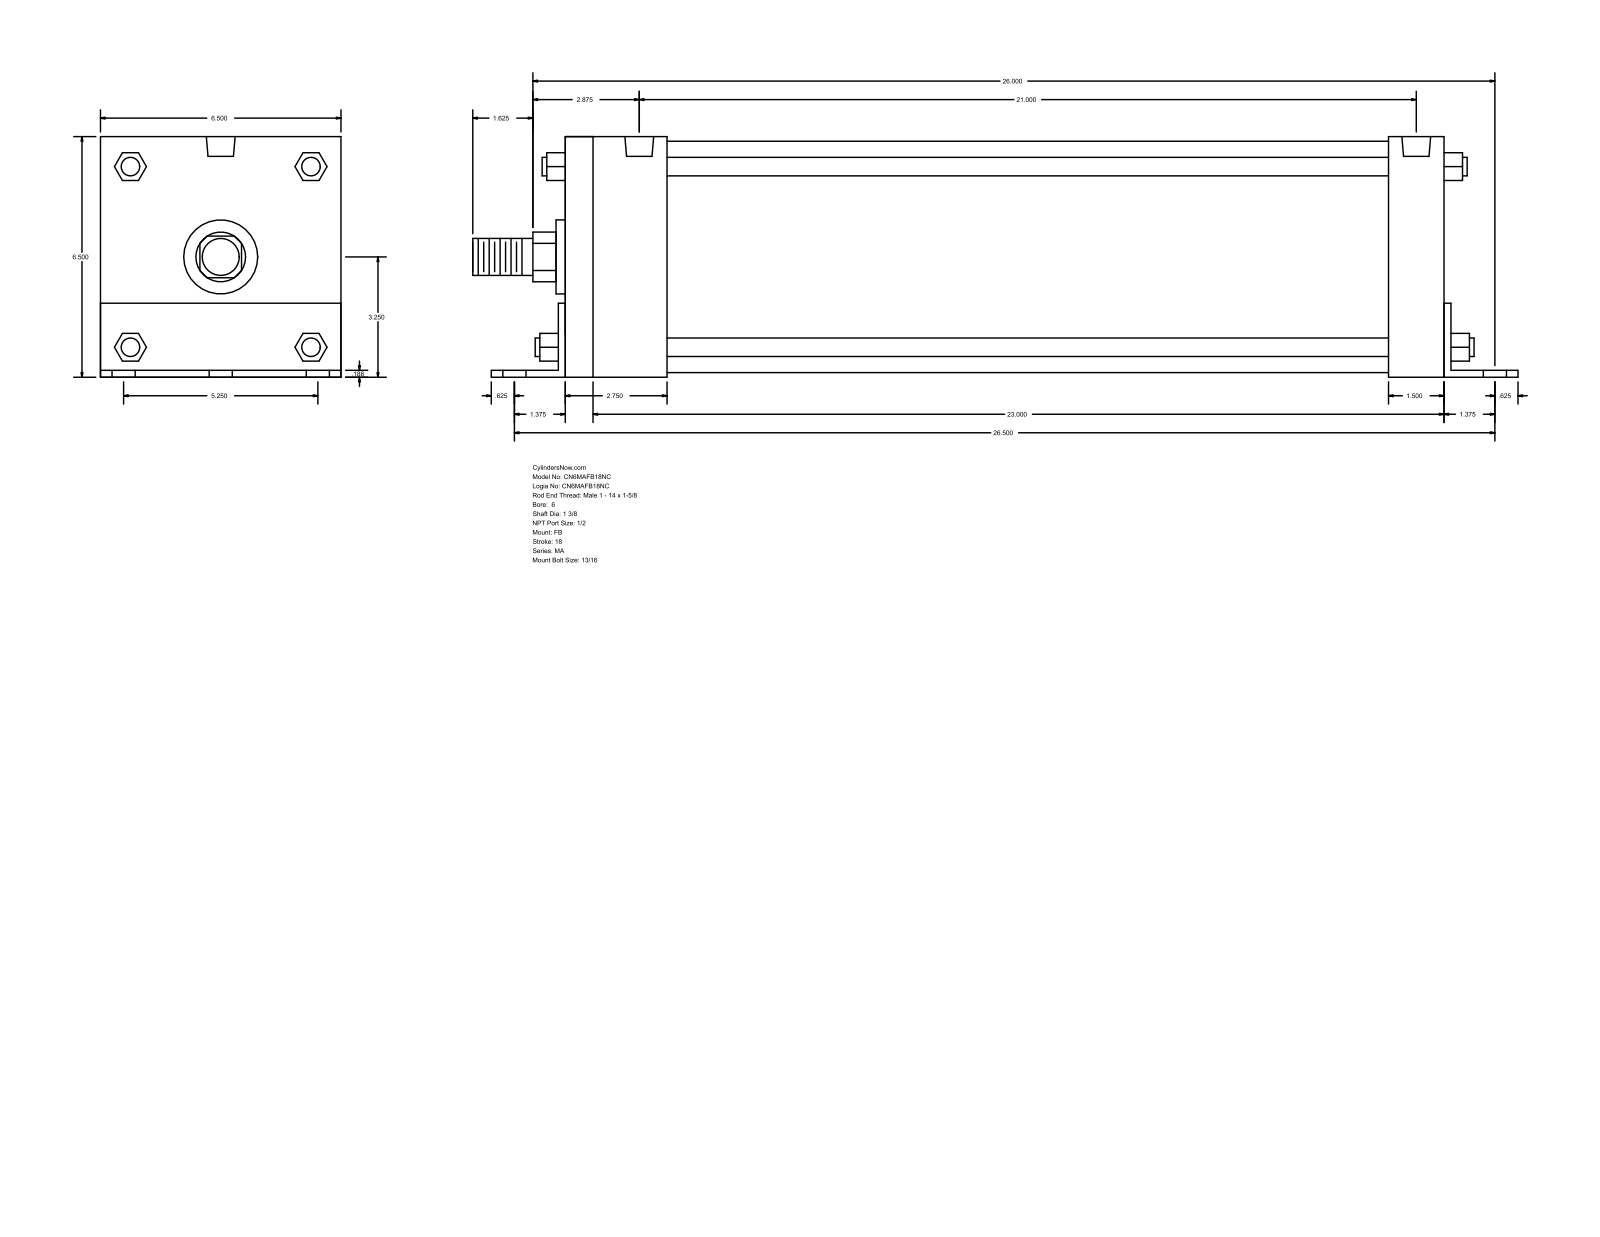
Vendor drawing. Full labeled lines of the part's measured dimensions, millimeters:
Part name (STEP PRODUCT): MA_FB__0600_1.375
STEP written by: GSSL Pune (CONFIG_CONTROL_DESIGN)
Units: millimetres
Bodies: 0 solids, 140 faces (105 planar, 35 cylindrical, 0 other)
Overall size (bounding box): 714.38 × 165.15 × 165.1
Round holes (diameter × count): ⌀20.64 ×6, ⌀17.46 ×4, ⌀19.77 ×2
Round bosses / shafts (diameter × count): ⌀12.7 ×4, ⌀158.75 ×1, ⌀50.8 ×1, ⌀34.92 ×1, ⌀25.4 ×1
Partial cylindrical surfaces — rounded edges, fillets, slot ends (radius × count): R17.06 ×1, R32.05 ×1
Main face-to-face distances: 165.1, 4.76, 600.07, 165.15, 4.71, 160.39, 4.77, 38.1, 42.86, 609.6
Hole centre spacings: 66.67, 673.24, 669.93, 83.82, 85.78, 108.6, 133.34, 530.22
